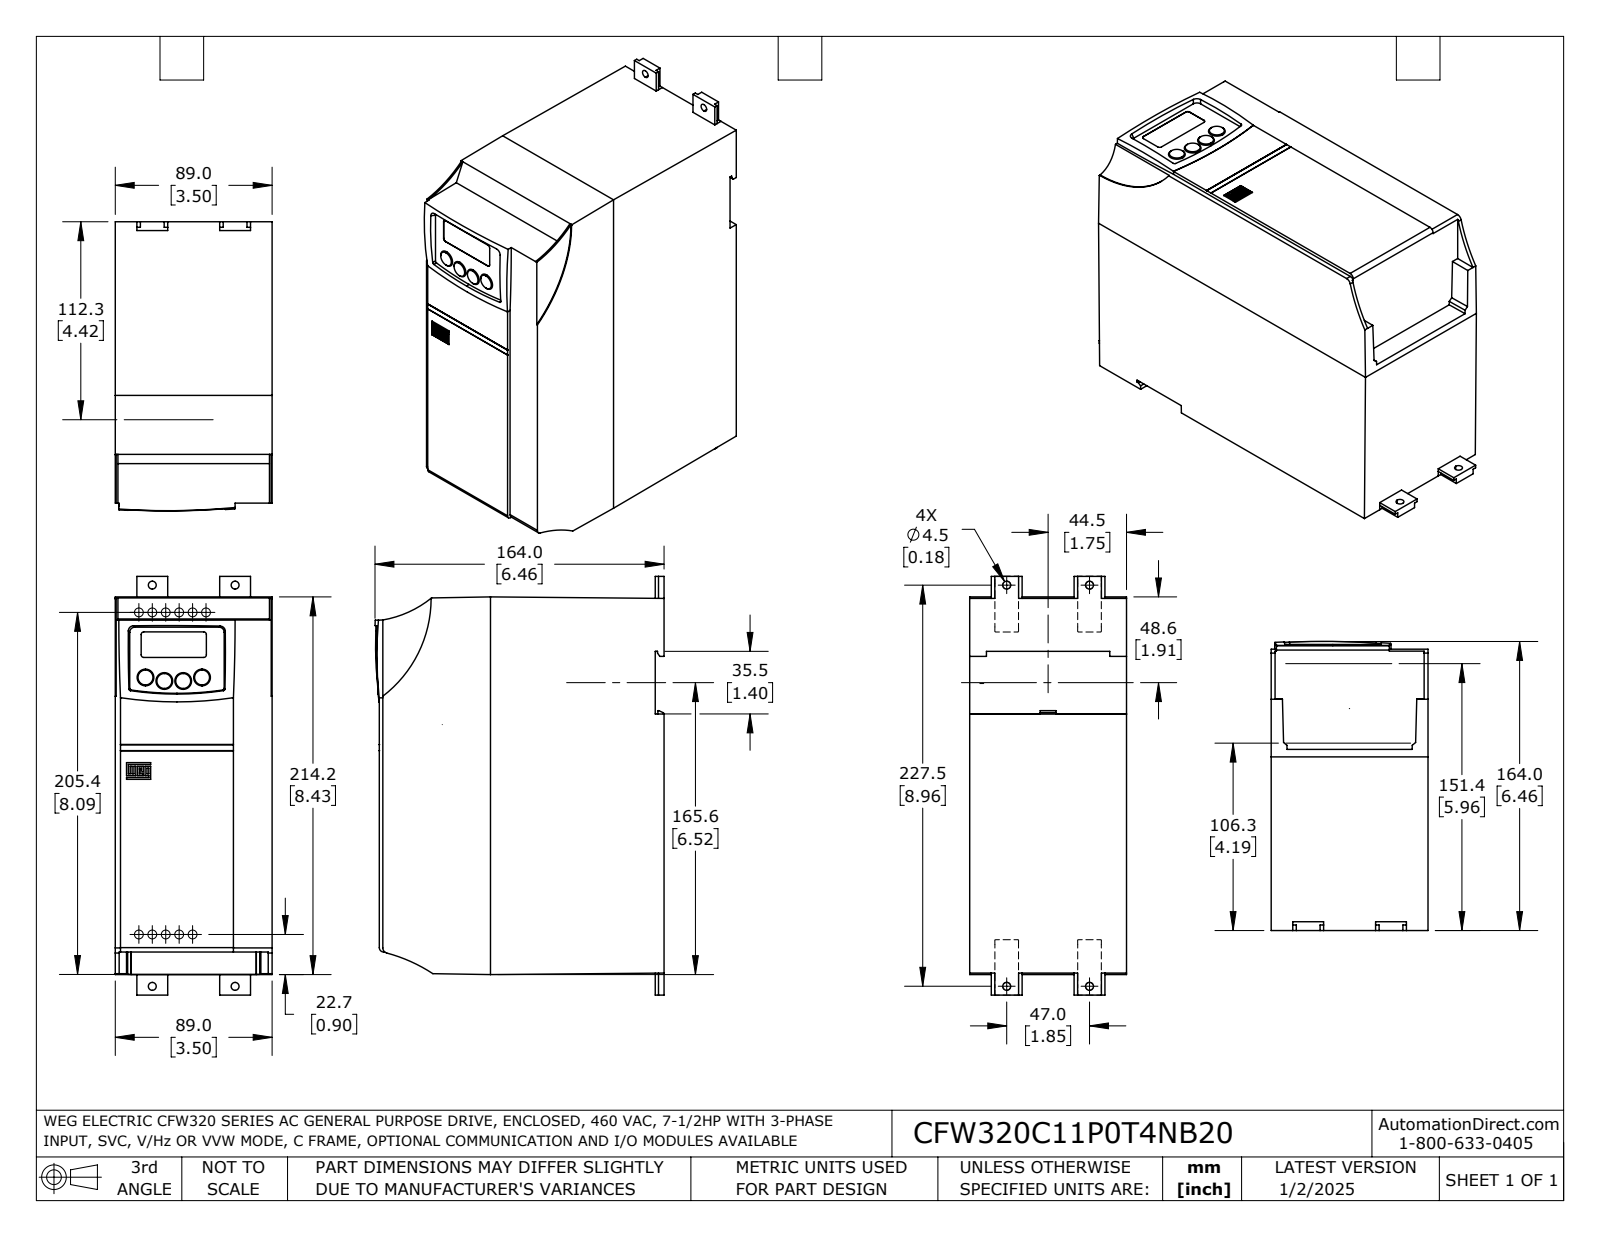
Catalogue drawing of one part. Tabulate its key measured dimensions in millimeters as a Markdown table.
| quantity | value |
| --- | --- |
| part name | CFW320C11P0T4NB20 |
| STEP written by | SolidWorks 2021 (AUTOMOTIVE_DESIGN) |
| units | millimeters |
| bodies | 1 solid, 206 faces (165 planar, 28 cylindrical, 13 other) |
| overall size | 237.5 × 164 × 89 |
| volume | 2 958 000 mm³ |
| surface area | 139 000 mm² |
| round holes (diameter × count) | 4.5 × 4 |
| partial cylindrical surfaces (radius × count) | 1.5 × 4, 3 × 3, 1017 × 2, 1 × 1, 2.5 × 1, 60 × 1, 69.9 × 1, 90 × 1 |
| main face-to-face distances | 89, 161.6, 2, 159.6, 5, 154.6, 156.6, 1, 0.5, 88.5 |
| hole center spacings | 47, 227.6, 232.4 |
